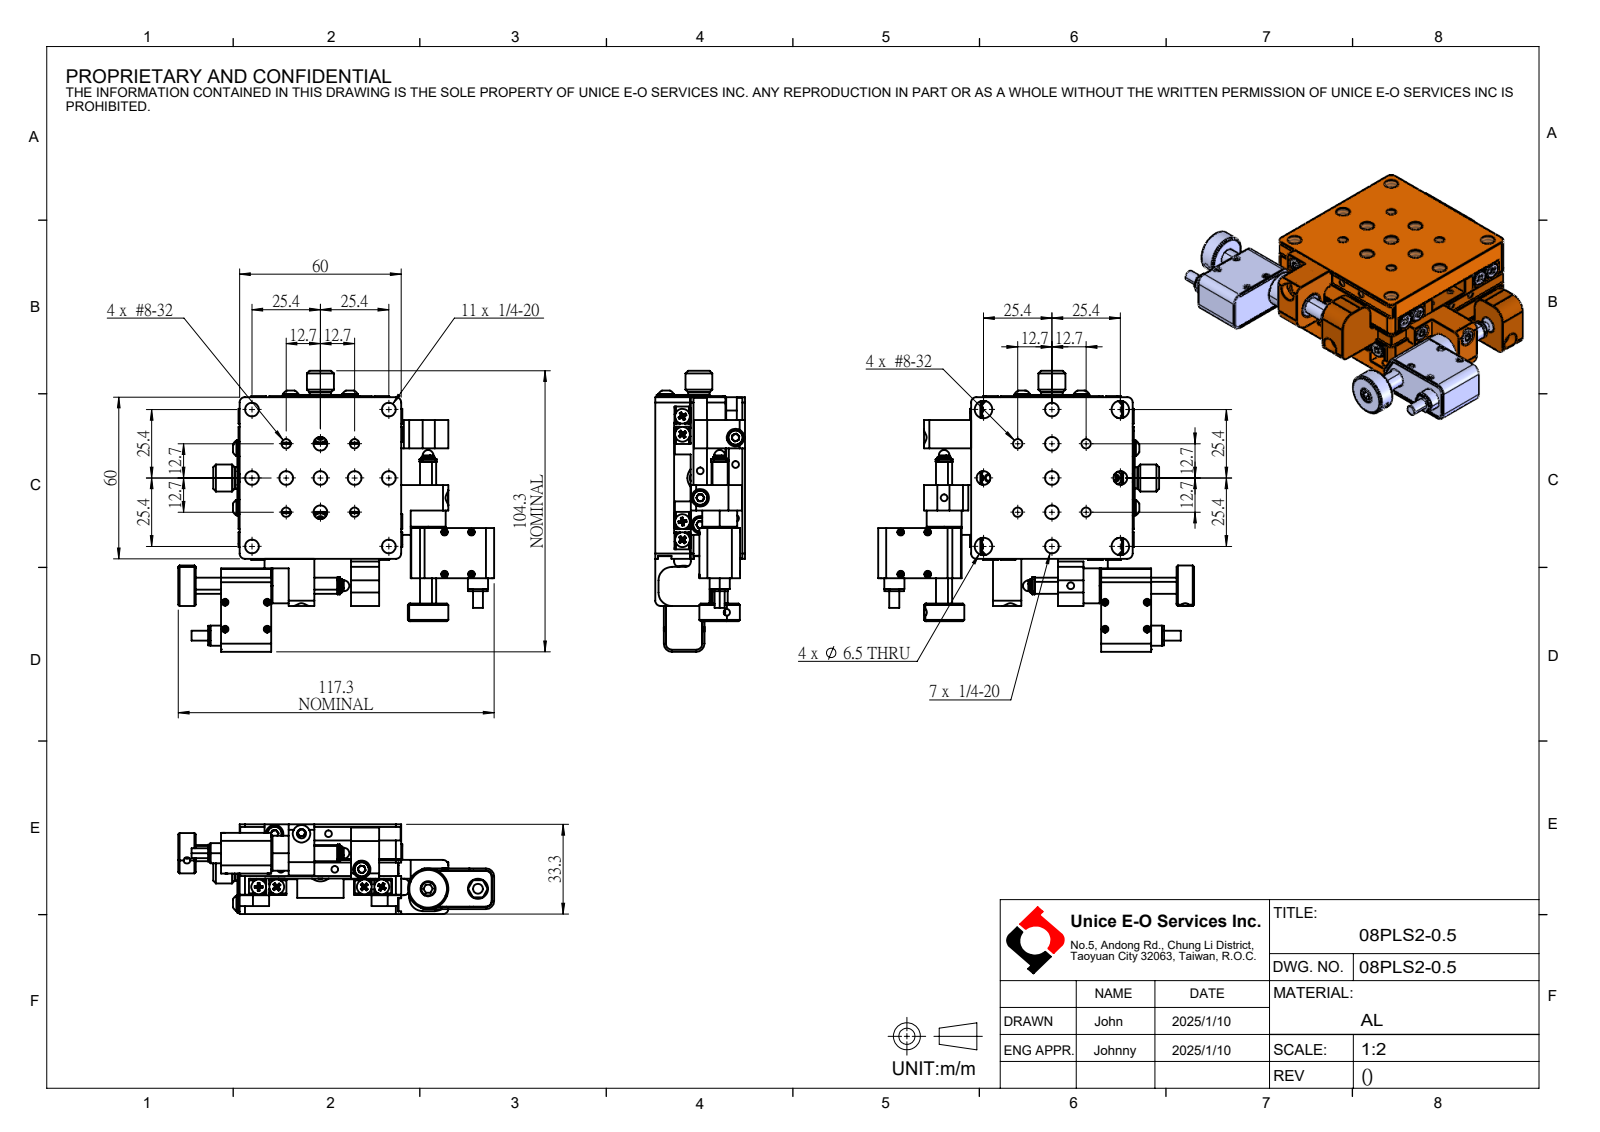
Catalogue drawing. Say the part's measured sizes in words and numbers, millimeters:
The part is named "08PLS2-0.5". Its 3-D file was written by "SolidWorks 2024 (CONFIG_CONTROL_DESIGN)". It is 0 solids with 3642 faces: 1284 planar, 995 cylindrical and 1363 other. Overall it measures 117.27 by 104.3 by 33.3 millimeters. Round holes: 40 of diameter 2.05, 33 of diameter 2.5, 26 of diameter 5, 24 of diameter 3, 13 of diameter 5.11, 10 of diameter 6.5, 6 of diameter 3.4, 4 of diameter 1.4, 4 of diameter 2, 4 of diameter 3.2, 4 of diameter 3.45, 4 of diameter 3.5. Round bosses or shafts: 20 of diameter 3, 16 of diameter 5.5, 6 of diameter 6, 4 of diameter 5.7, 4 of diameter 2, 4 of diameter 1.4, 2 of diameter 15, 2 of diameter 10. Partial cylindrical surfaces (rounded edges, fillets, slot ends): 18 of radius 2, 8 of radius 5, 4 of radius 1.75, 4 of radius 3, 4 of radius 6. The main face-to-face distances are 13.1, 13.2, 7, 6.1, 7.1, 20.2, 6, 20.1, 13, 26.2. The hole center spacings are 28.4, 17.96, 25.4, 20, 12.7, 40.16, 10, 35.92.
